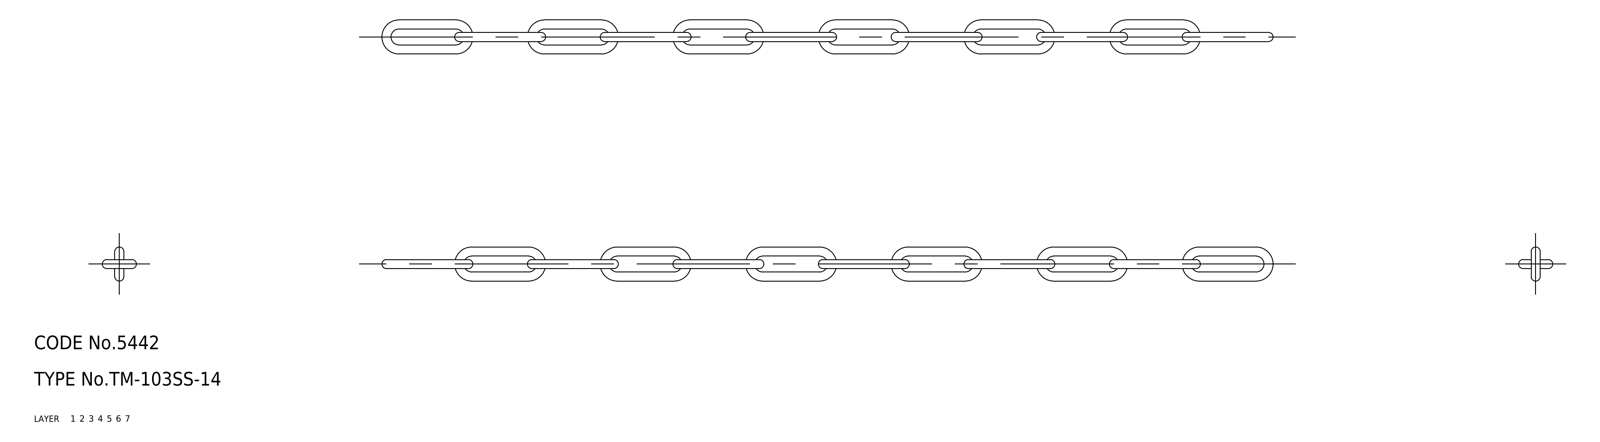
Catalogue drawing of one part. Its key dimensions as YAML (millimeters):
part_name: "chain; TM_103SS_14_11351_36"
step_written_by: "CADfix (AUTOMOTIVE_DESIGN)"
units: millimeters
bodies: {solids: 12, faces: 96, planar: 0, cylindrical: 0, other: 96}
overall_size: [196, 7.5, 7.5]
volume: 1600
surface_area: 3191
